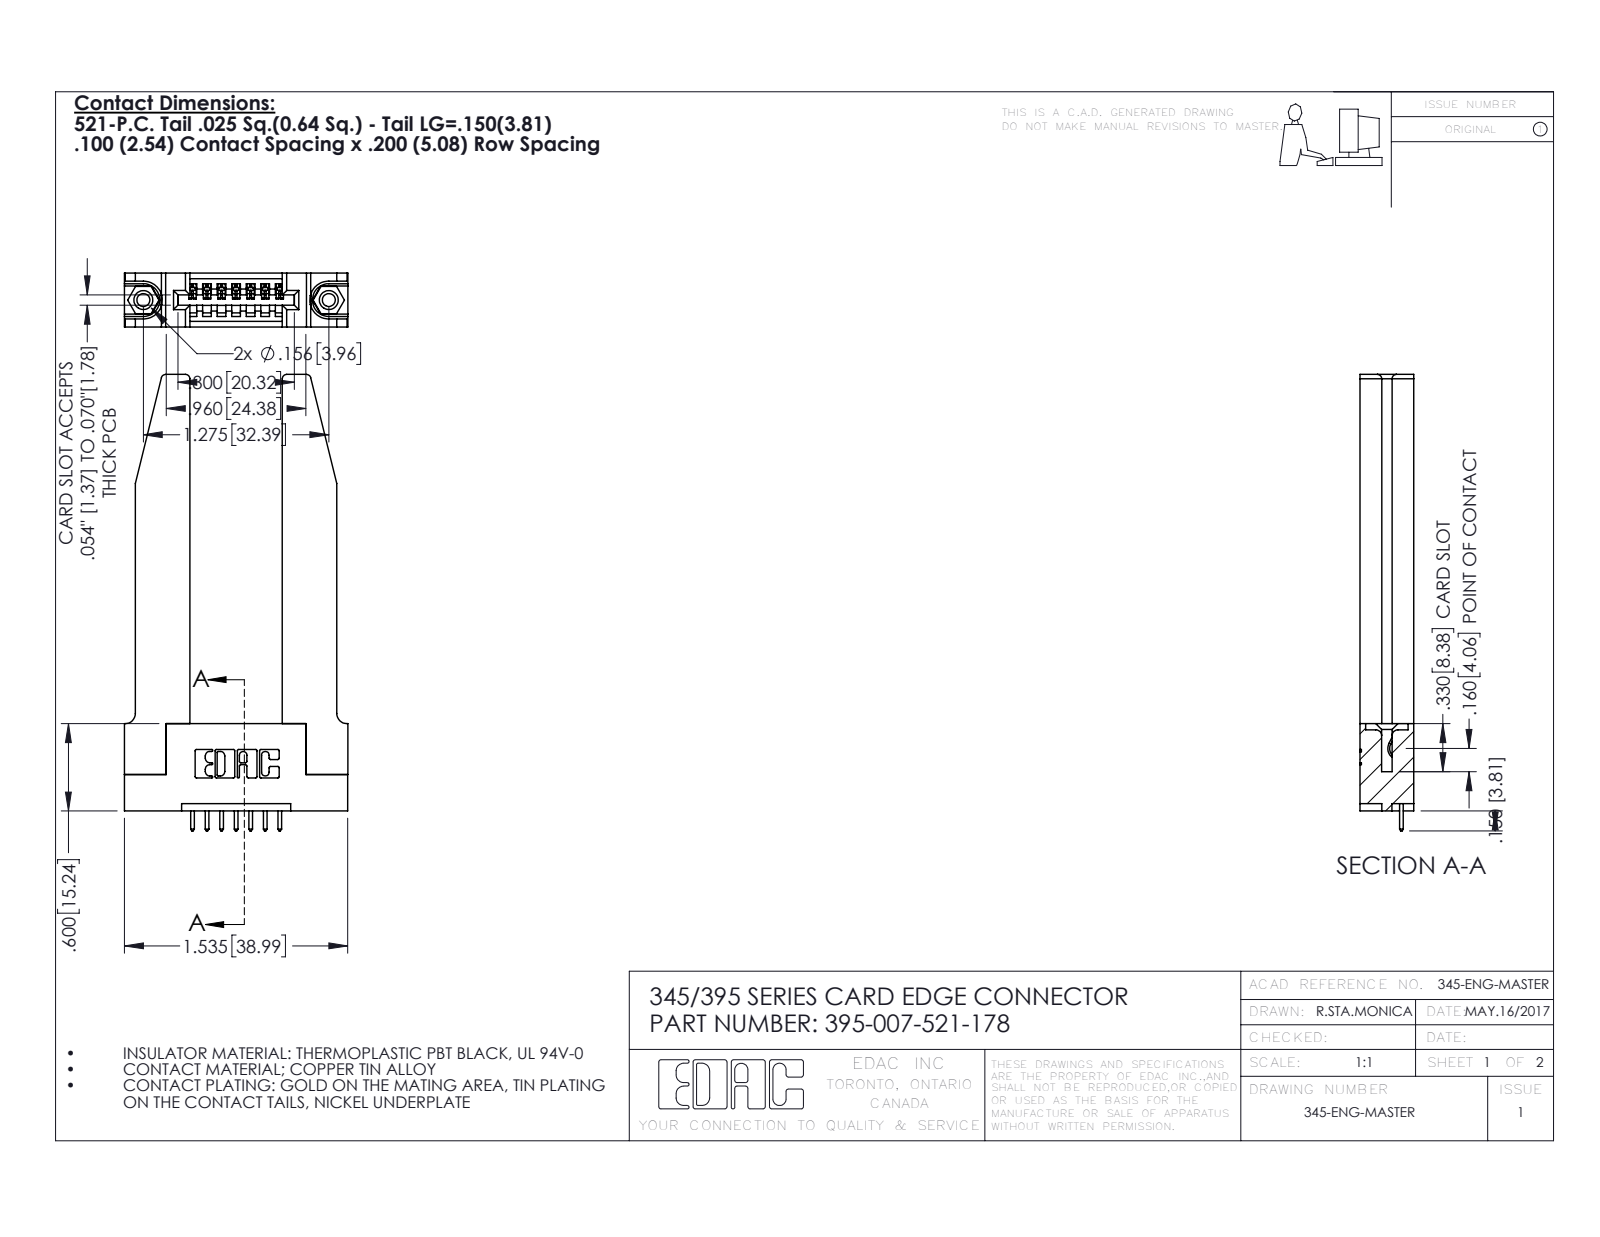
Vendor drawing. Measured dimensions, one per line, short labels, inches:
name: 395-007-521-178; 345-250-001_345-250-001-102; 345 Part_Flush Mounting Lugs - 0.156 Dia-TH; 345-292-001_345-293-121 (+1 more)
written by: SolidWorks 2016 (CONFIG_CONTROL_DESIGN)
unit: in
bodies: 12 solids, 766 faces (502 planar, 212 cylindrical, 52 other)
size: 3.137 × 1.536 × 0.37
volume: 0.682 in³; area: 16.75 in²
holes: 2× ⌀0.089, 2× ⌀0.125, 2× ⌀0.156, 1× ⌀0.064
bosses: 2× ⌀0.155
rounds: 22× R0.01, 14× R0.006, 14× R0.01, 8× R0.03, 6× R0.007, 6× R0.031, 3× R0.026, 2× R0.031
face distances: 0.37, 0.15, 0.22, 0.072, 0.148, 0.635, 0.077, 0.298, 0.2, 0.095
hole spacings: 0.27, 1.045, 1.275
